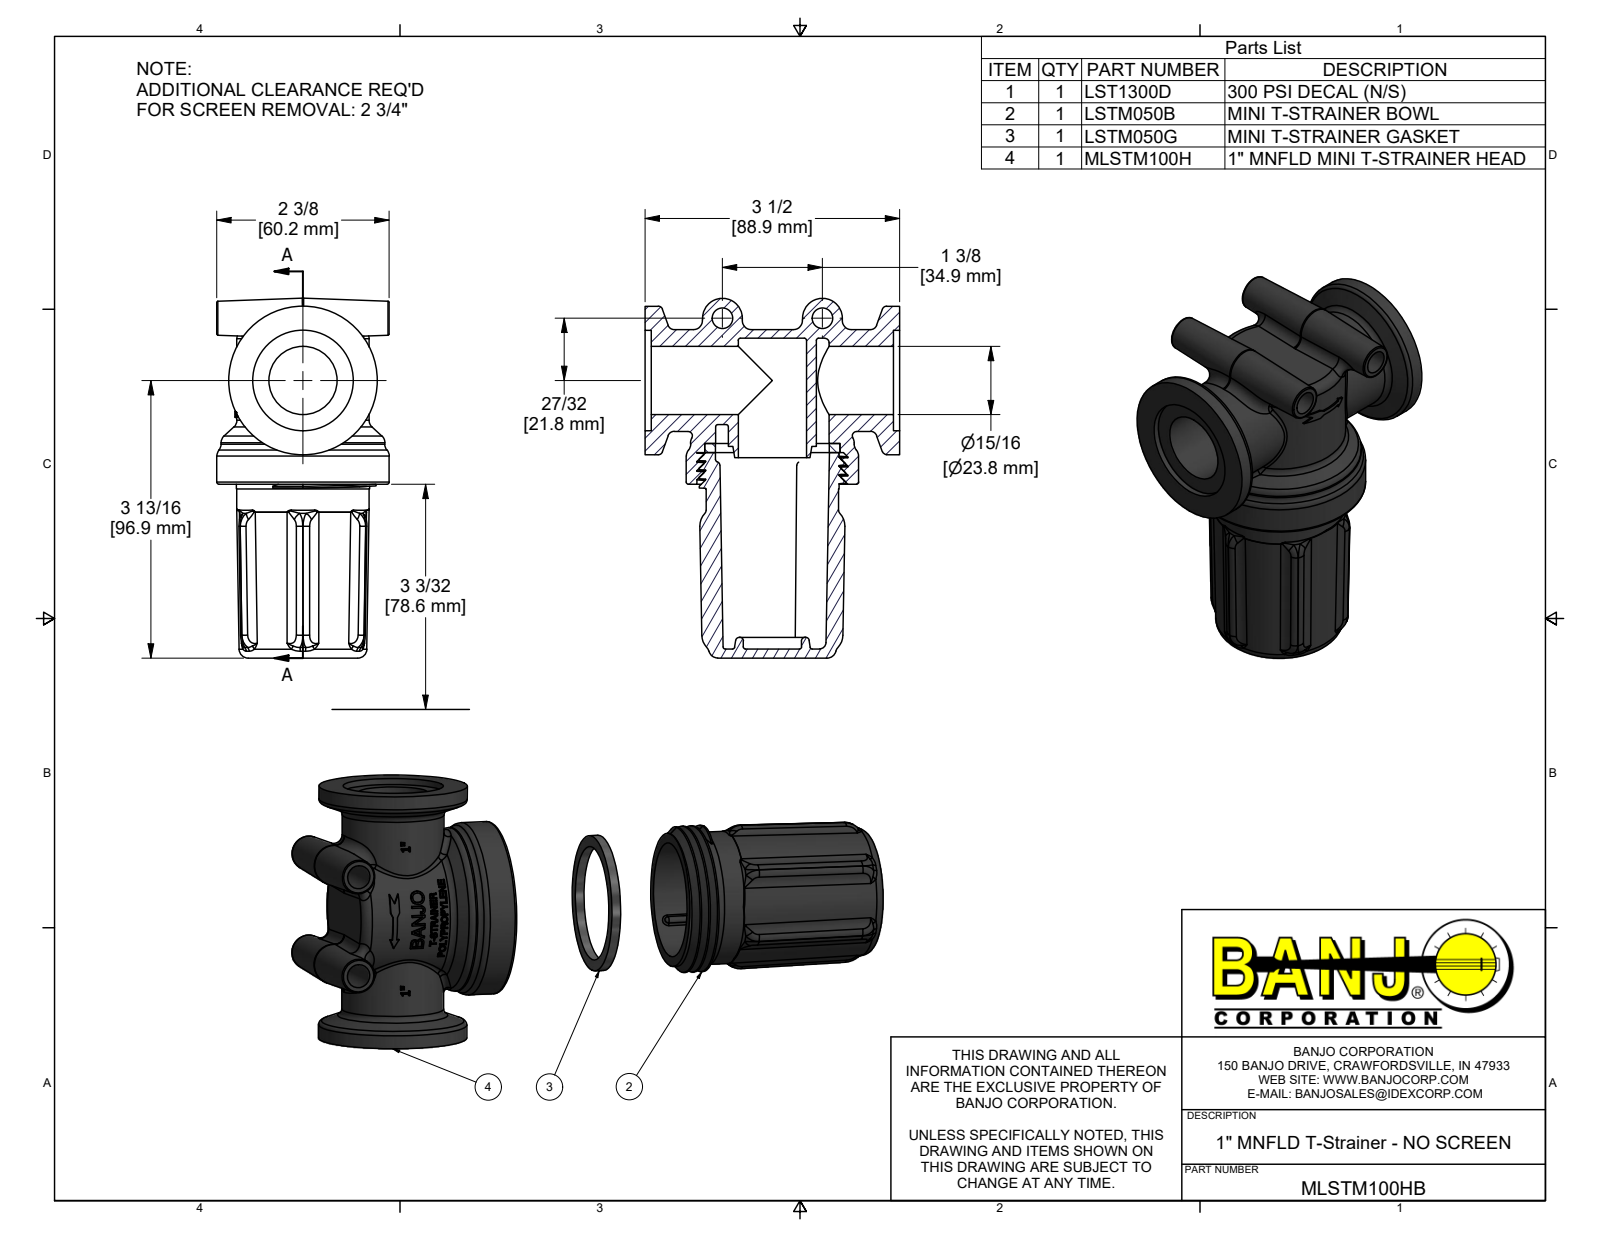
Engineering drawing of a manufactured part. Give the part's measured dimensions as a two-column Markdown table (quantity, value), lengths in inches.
| quantity | value |
| --- | --- |
| part name | MLSTM100HB; MLSTM100H; LSTM050G; LSTM050B |
| STEP written by | Autodesk Inventor 2019 (AUTOMOTIVE_DESIGN) |
| units | inches |
| bodies | 3 solids, 788 faces (299 planar, 97 cylindrical, 392 other) |
| overall size | 4.947 × 3.5 × 2.37 |
| volume | 8.623 in³ |
| surface area | 110.8 in² |
| round holes (diameter × count) | 0.937 × 2, 0.8 × 1, 1.38 × 1, 1.56 × 1, 1.563 × 1, 1.891 × 1, 2.073 × 1 |
| round bosses / shafts (diameter × count) | 2.37 × 1, 2.25 × 1, 2.04 × 1, 2.01 × 1, 1.861 × 1, 1.86 × 1, 1.833 × 1, 1.82 × 1 |
| partial cylindrical surfaces (radius × count) | 0.03 × 4, 0.05 × 3, 0.55 × 1, 0.605 × 1, 0.609 × 1, 0.73 × 1 |
| main face-to-face distances | 2.825, 3.5, 0.125, 0.084, 3.416, 2.95, 4.515, 1.69, 1.565, 4.397 |
